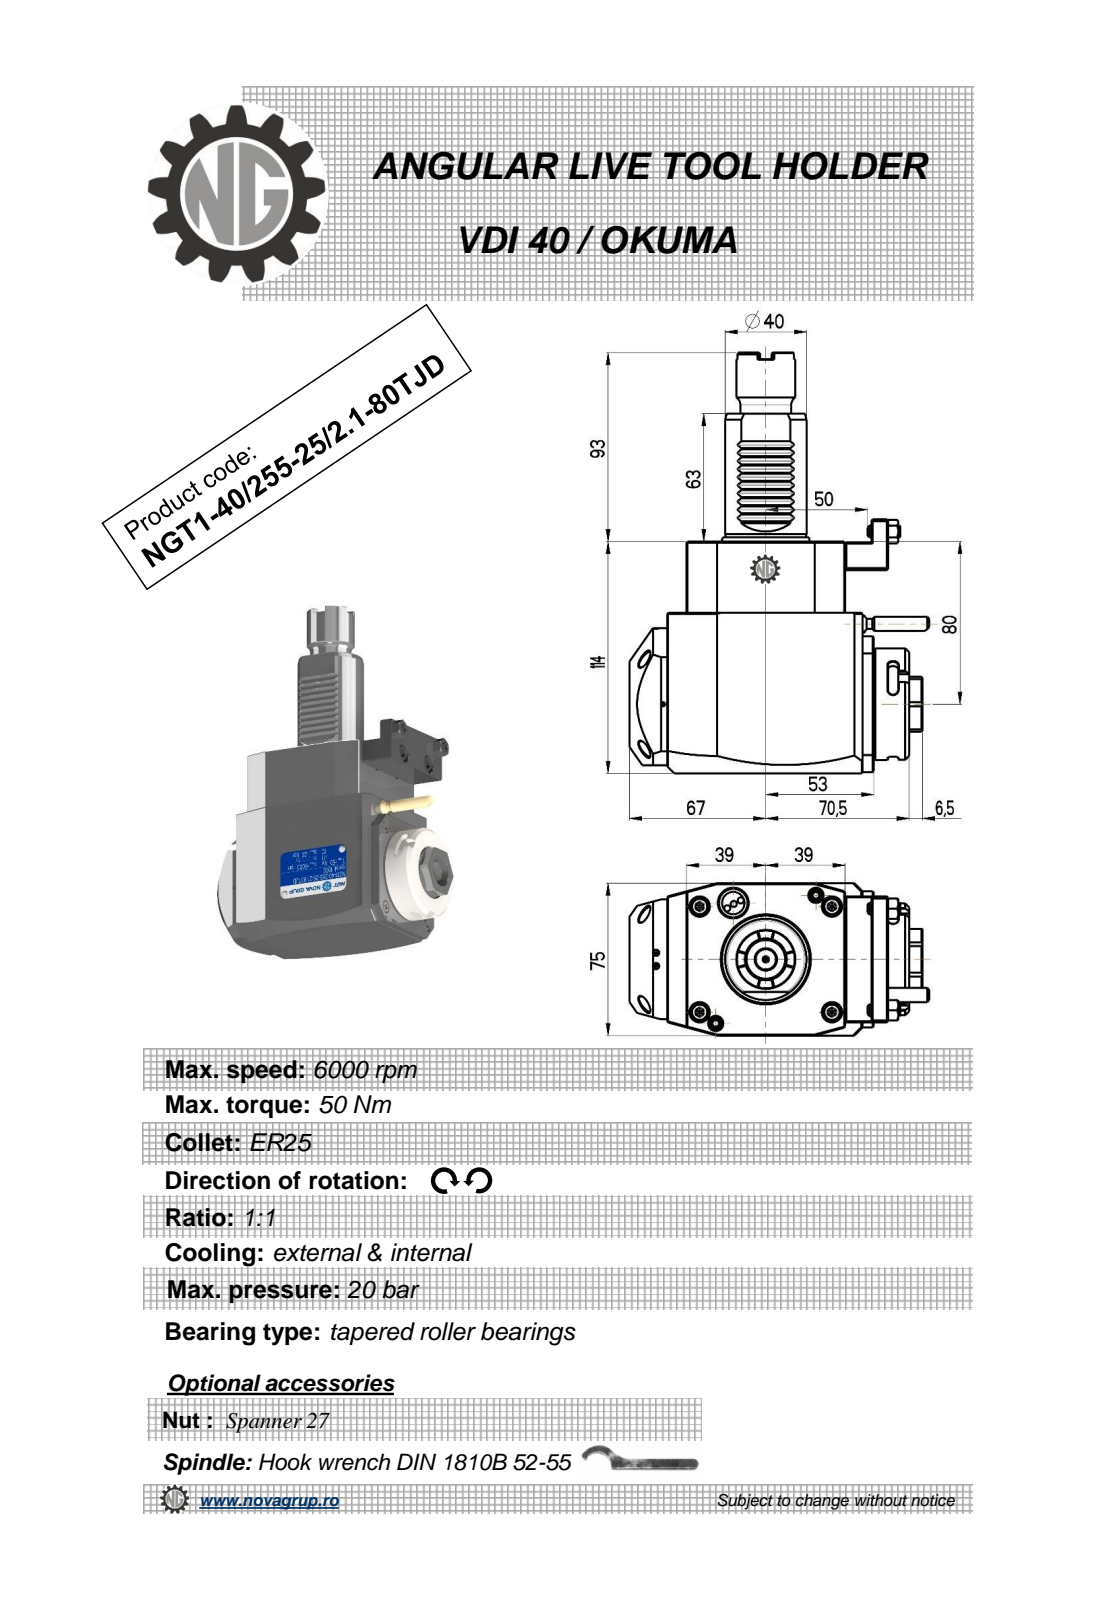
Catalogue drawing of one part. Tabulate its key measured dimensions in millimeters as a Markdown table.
| quantity | value |
| --- | --- |
| part name | NGT1_40_255_25_1_1_80TJD |
| STEP written by | PRO/ENGINEER BY PARAMETRIC TECHNOLOGY CORPORATION, 2010280 (CONFIG_CONTROL_DESIGN) |
| units | millimeters |
| bodies | 1 solid, 398 faces (194 planar, 76 cylindrical, 128 other) |
| overall size | 207 × 147.33 × 75 |
| volume | 988 755 mm³ |
| surface area | 75 451 mm² |
| round holes (diameter × count) | 2.5 × 1, 3 × 1, 18 × 1 |
| round bosses / shafts (diameter × count) | 6 × 2, 55 × 1, 48 × 1, 40 × 1, 29 × 1, 25 × 1, 8.96 × 1, 7 × 1 |
| partial cylindrical surfaces (radius × count) | 0.3 × 10, 0.31 × 10, 2.5 × 6, 180 × 2, 0.5 × 1, 10 × 1, 15 × 1, 24.5 × 1 |
| main face-to-face distances | 75, 114, 14, 21, 109.5, 92, 17.5, 0.5, 18.5, 31.5 |
| hole center spacings | 43.2 |
